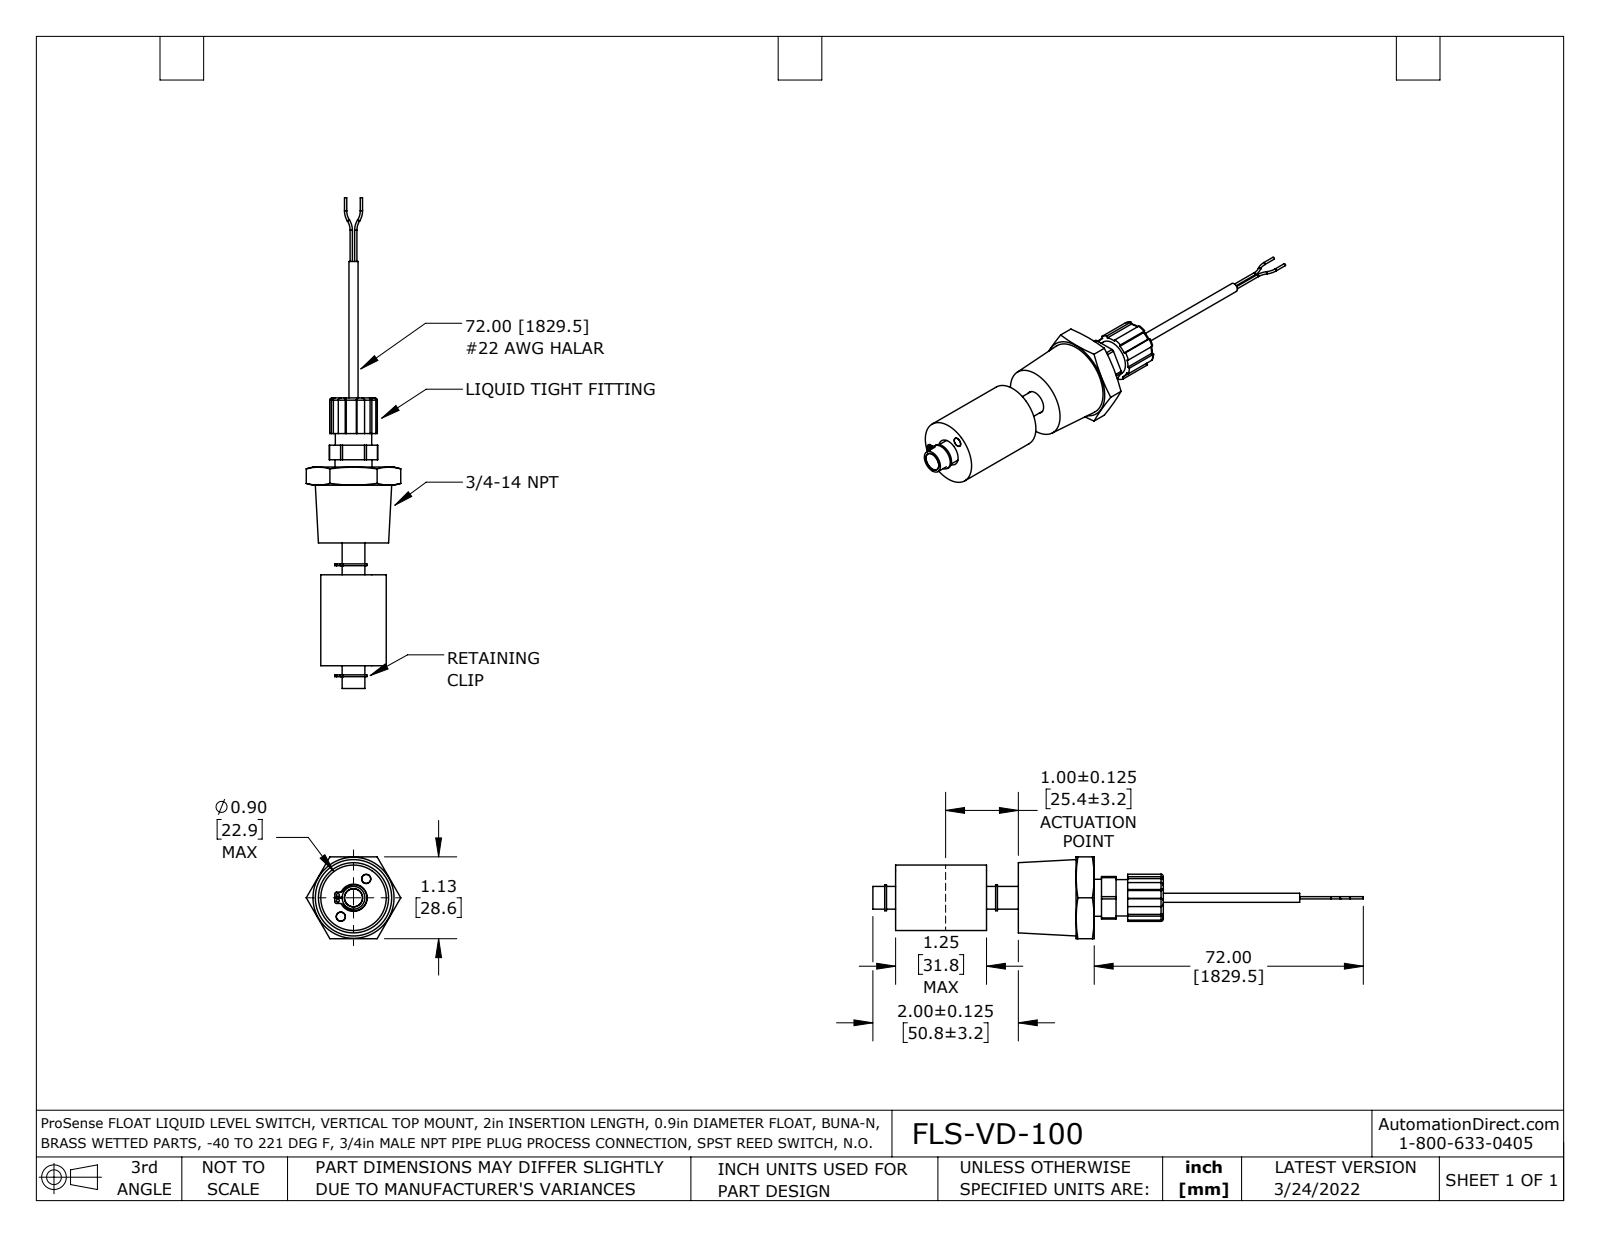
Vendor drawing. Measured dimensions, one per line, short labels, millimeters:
name: ADM4168-1 nc coord fxt
written by: SolidWorks 2021 (AUTOMOTIVE_DESIGN)
unit: mm
bodies: 13 solids, 219 faces (74 planar, 109 cylindrical, 36 other)
size: 171.3 × 33 × 28.6
volume: 29 690 mm³; area: 15 870 mm²
holes: 2× ⌀1, 1× ⌀6.3, 1× ⌀7.1, 1× ⌀7.4, 1× ⌀9.5
bosses: 6× ⌀0.8, 3× ⌀3.2, 1× ⌀22.9, 1× ⌀12.7, 1× ⌀9, 1× ⌀8, 1× ⌀6.4
rounds: 16× R0.8, 2× R0.7, 2× R1.2, 1× R7.6, 1× R8.3
face distances: 31.8, 26.5, 69.4, 42.9, 37.6, 11.1, 28.6, 6.9, 21.7, 61.7
hole spacings: 5.6, 2
